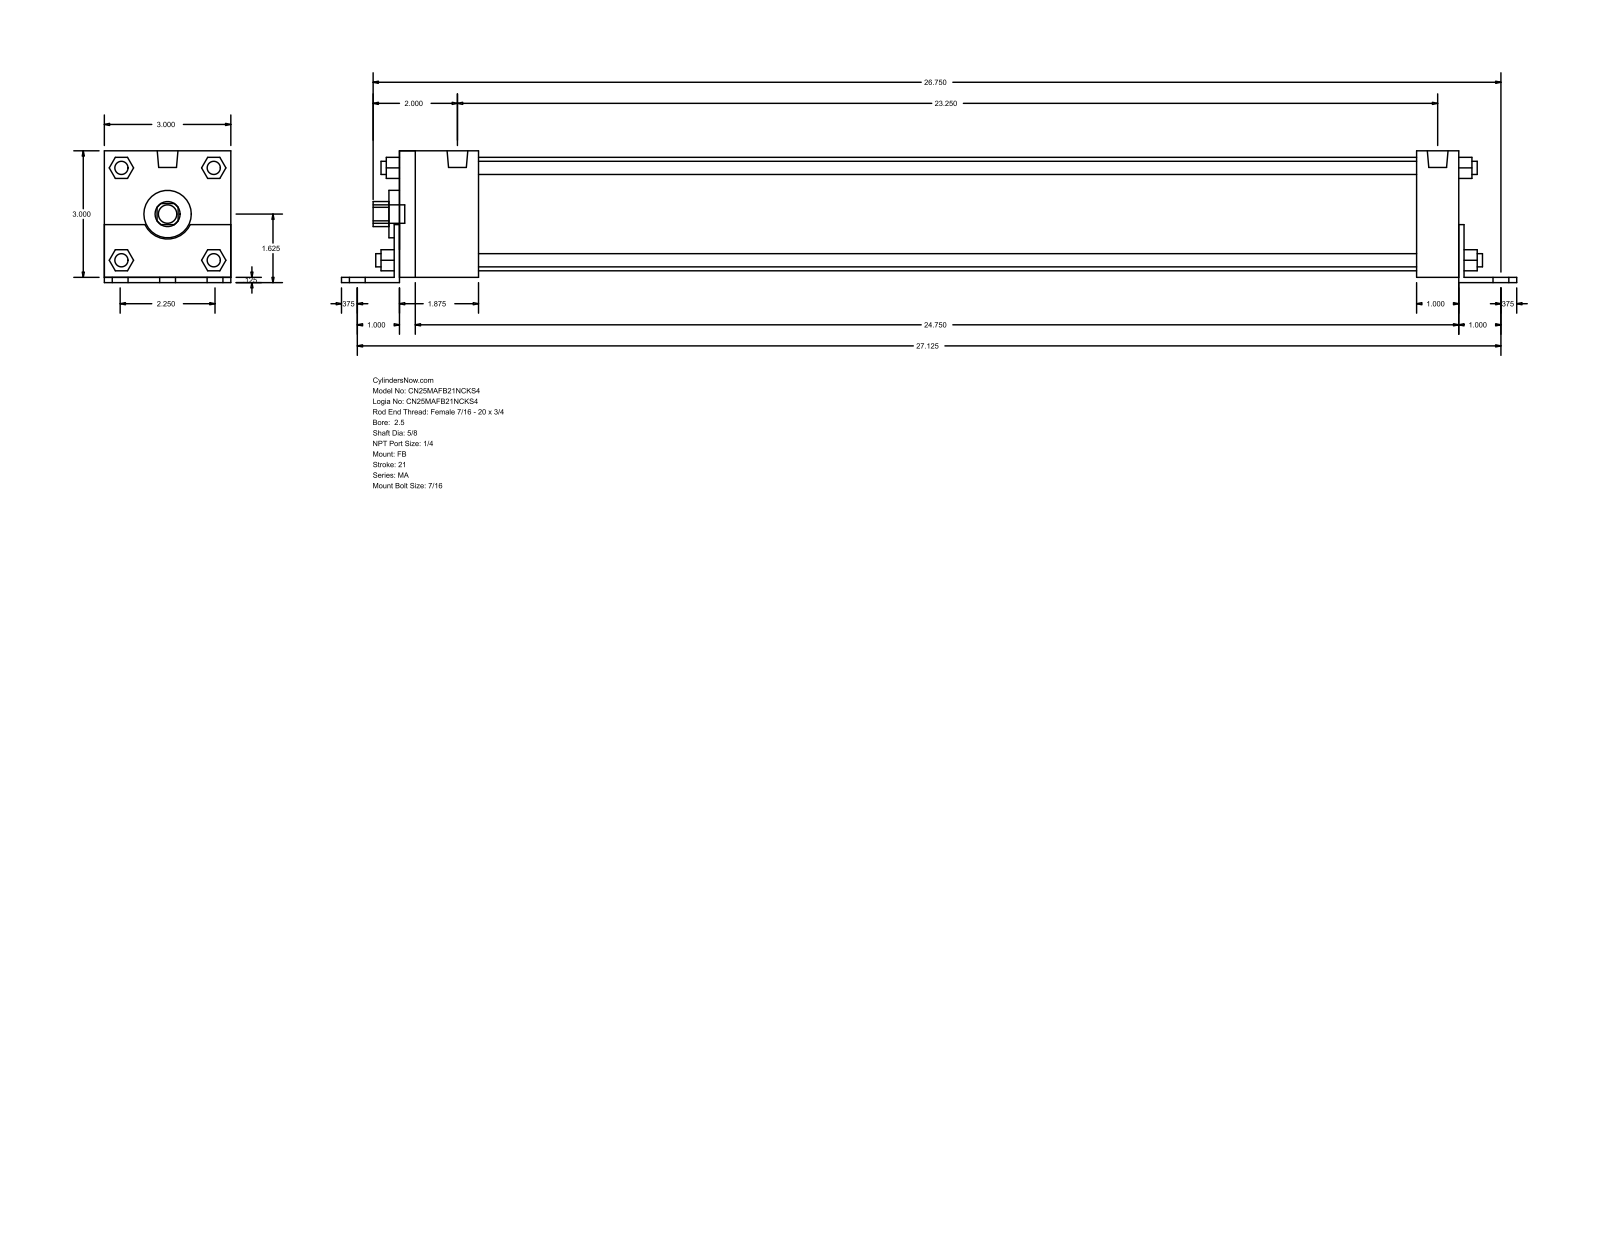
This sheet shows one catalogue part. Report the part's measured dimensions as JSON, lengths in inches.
{"part_name": "MA_FB__0250_0.625", "step_written_by": "GSSL Pune (CONFIG_CONTROL_DESIGN)", "units": "inches", "bodies": {"solids": 0, "faces": 140, "planar": 105, "cylindrical": 35, "other": 0}, "overall_size": [27.875, 3.125, 3], "round_holes": [[0.625, 1], [1.125, 1], [2.69, 1]], "round_bosses_or_shafts": [[0.313, 8], [0.437, 7], [0.492, 2]], "partial_cylinders_radius": [[0.297, 1], [0.593, 1]], "face_to_face_distances": [3, 0.125, 3.125, 0.125, 25.25, 25.125, 1.125, 1.875, 1, 25.375]}
